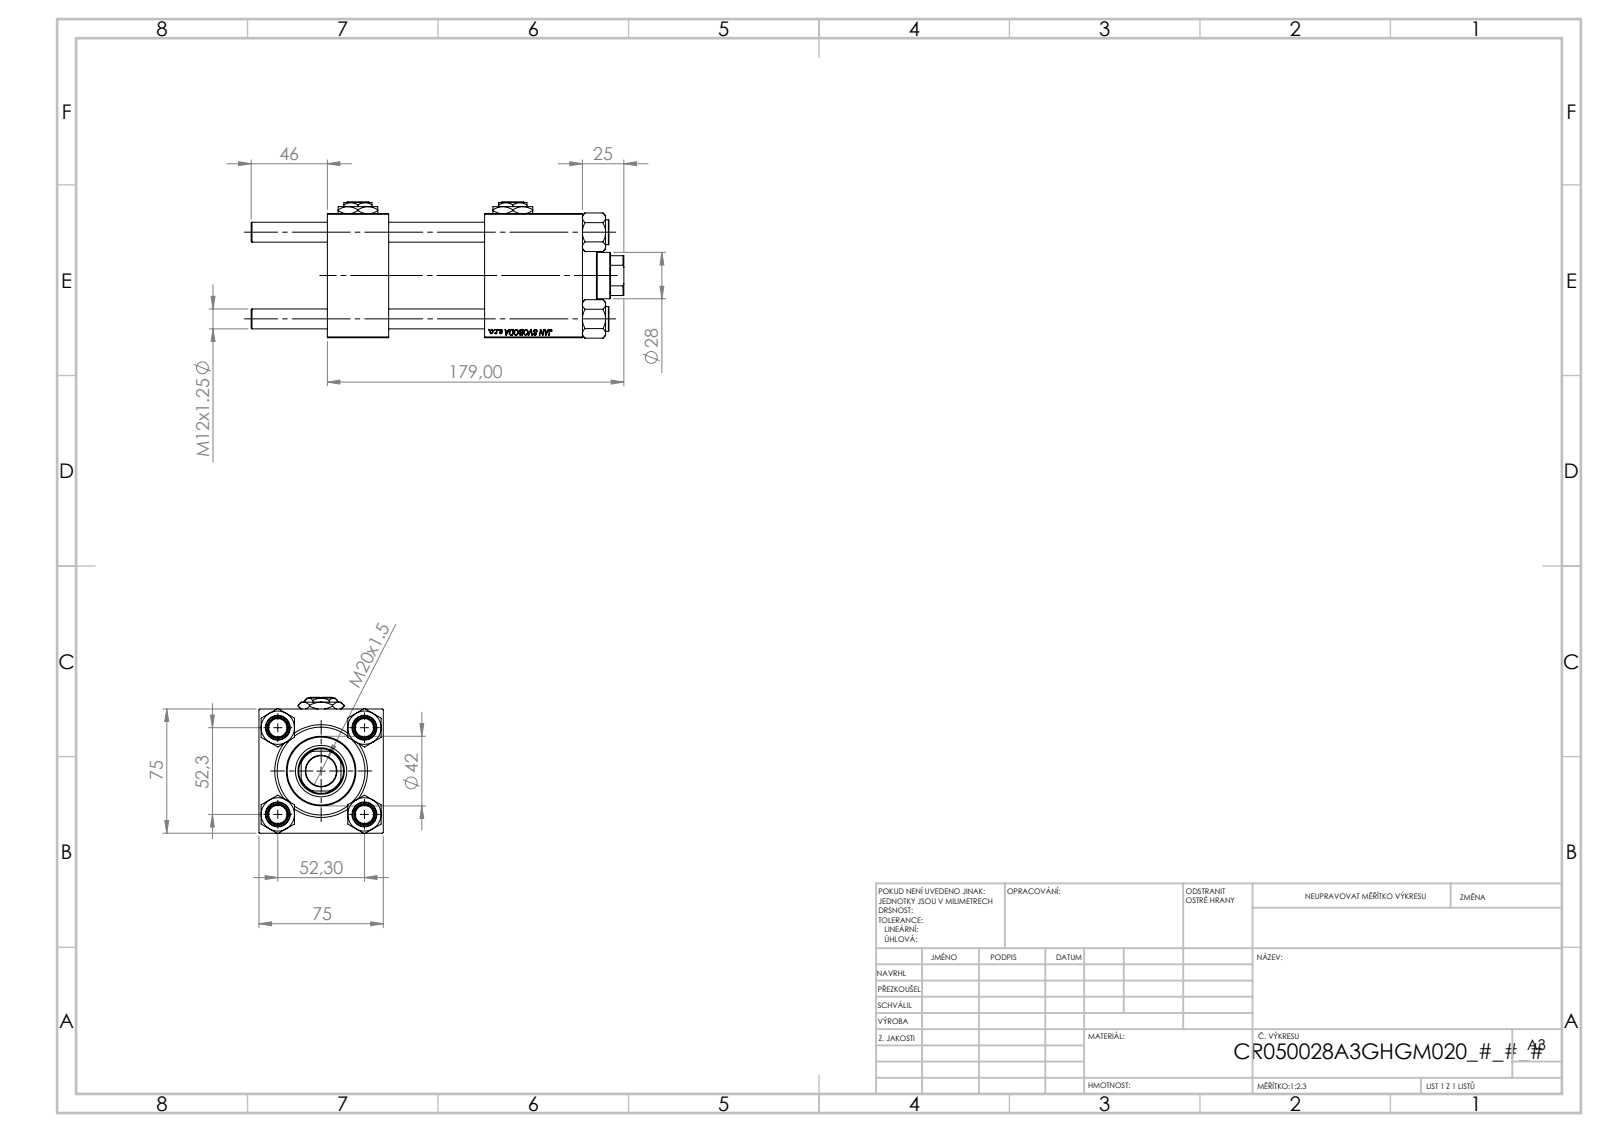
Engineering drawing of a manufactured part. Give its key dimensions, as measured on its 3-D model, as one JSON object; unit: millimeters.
{"part_name": "CR025_012_A_0_G_A_G_M_020_+#_##_TYCINKA; V215_VC_A; NUT_M5; V215CR_BODY_A (+2 more)", "step_written_by": "SolidWorks 2019 (CONFIG_CONTROL_DESIGN)", "units": "millimeters", "bodies": {"solids": 13, "faces": 1233, "planar": 567, "cylindrical": 88, "other": 578}, "overall_size": [225, 82.27, 75], "volume_mm3": 697084, "surface_area_mm2": 171866, "round_holes": [[12, 4], [7, 2], [20.96, 2], [30, 2], [18.5, 1], [28, 1], [31, 1], [41, 1], [50, 1], [53, 1]], "round_bosses_or_shafts": [[15, 4], [56, 1], [42, 1]], "partial_cylinders_radius": [[13.5, 1]], "face_to_face_distances": [75, 37, 154, 117, 95, 59, 58, 125.3, 88.3, 30.3], "hole_center_spacings": [36.98, 52.3, 73.96, 93.5]}
